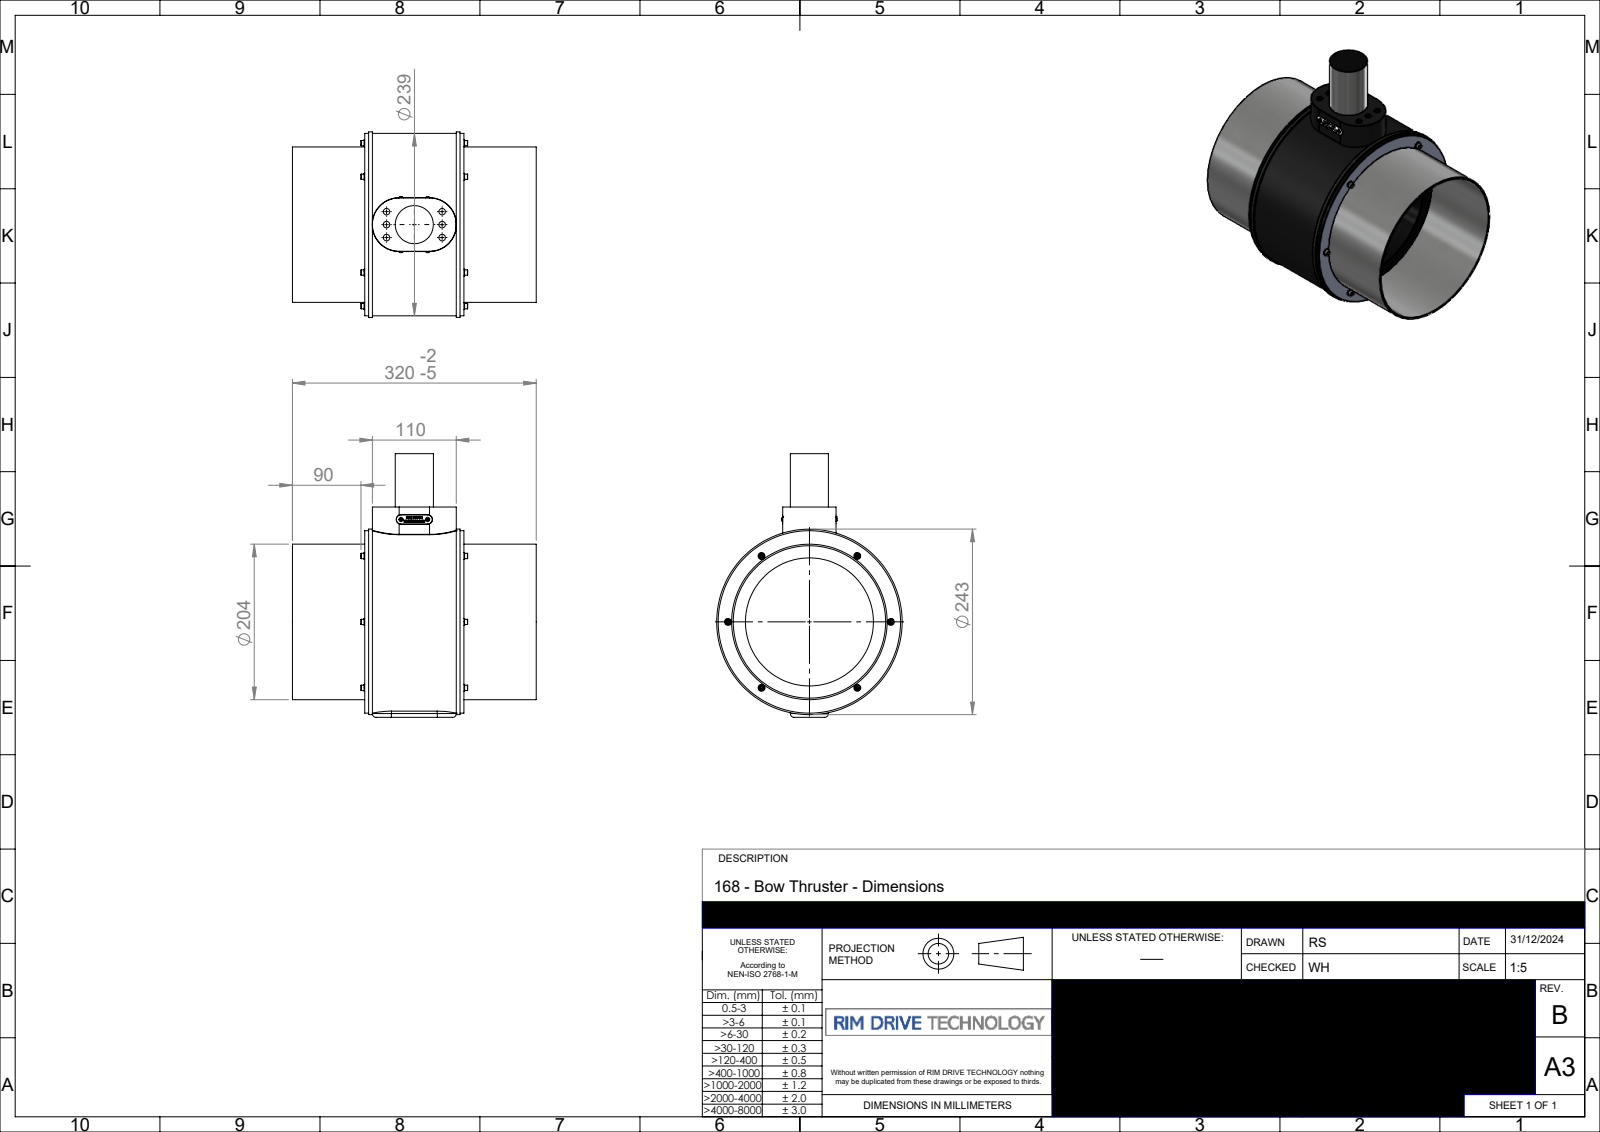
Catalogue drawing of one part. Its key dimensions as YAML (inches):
part_name: "P-168-030-rev-B-BT"
step_written_by: "SolidWorks 2024 (AUTOMOTIVE_DESIGN)"
units: inches
bodies: {solids: 1, faces: 904, planar: 621, cylindrical: 99, other: 184}
overall_size: [13.616, 12.601, 9.583]
volume: 208.8
surface_area: 759.3
round_holes:
  - {diameter: 0.181, count: 6}
  - {diameter: 0.335, count: 6}
  - {diameter: 0.138, count: 2}
  - {diameter: 6.614, count: 1}
  - {diameter: 7.874, count: 1}
round_bosses_or_shafts:
  - {diameter: 0.354, count: 6}
  - {diameter: 0.276, count: 6}
  - {diameter: 0.157, count: 6}
  - {diameter: 0.38, count: 2}
  - {diameter: 0.224, count: 2}
  - {diameter: 0.118, count: 2}
  - {diameter: 9.583, count: 1}
  - {diameter: 9.425, count: 1}
partial_cylinders:
  - {radius: 0.02, count: 2}
  - {radius: 0.197, count: 2}
  - {radius: 0.242, count: 2}
  - {radius: 0.246, count: 2}
  - {radius: 0.984, count: 2}
  - {radius: 1.358, count: 2}
  - {radius: 1.378, count: 2}
face_to_face_distances: [4.727, 0.394, 5.12, 4.333, 0.197, 10.86, 2.756, 4.924, 4.53, 3.74]
hole_center_spacings: [0.669, 2.951, 4.209, 7.502, 2.874, 8.419, 1.339, 3.17]
